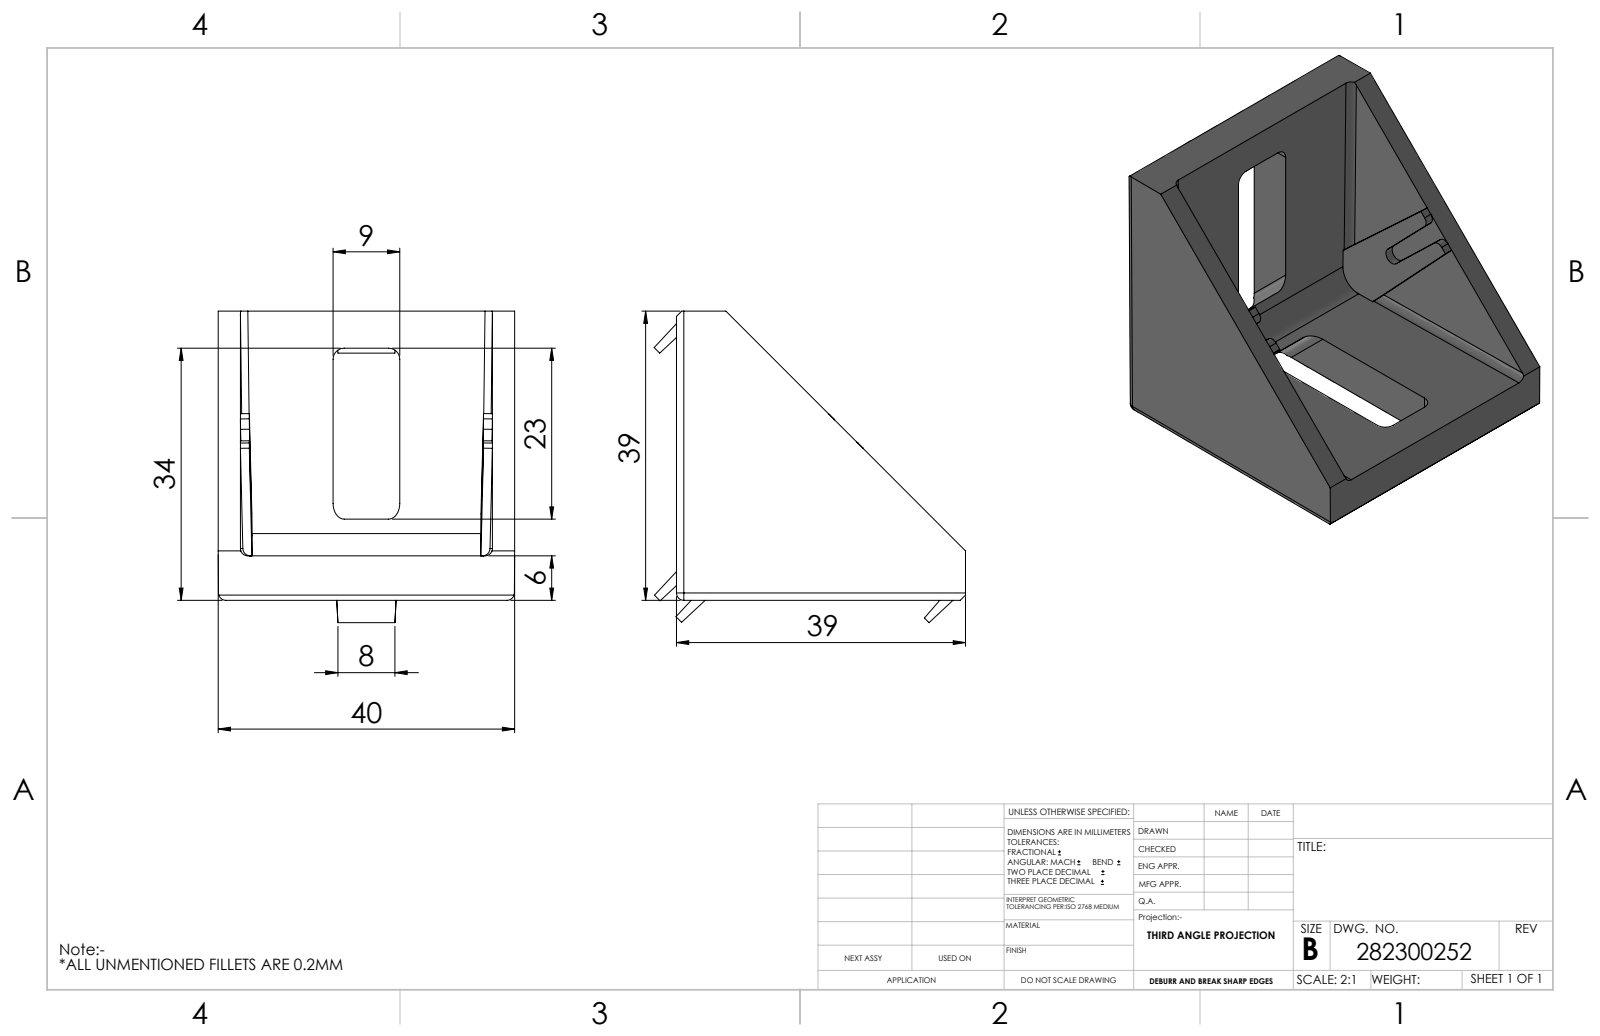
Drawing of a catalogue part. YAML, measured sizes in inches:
part_name: "282300252"
step_written_by: "SolidWorks 2014 (AUTOMOTIVE_DESIGN)"
units: inches
bodies: {solids: 1, faces: 189, planar: 103, cylindrical: 68, other: 18}
overall_size: [2.132, 1.575, 1.335]
volume: 0.914
surface_area: 15.96
round_bosses_or_shafts:
  - {diameter: 0.157, count: 4}
partial_cylinders:
  - {radius: 0.039, count: 33}
  - {radius: 0.02, count: 12}
  - {radius: 0.059, count: 8}
  - {radius: 0.044, count: 2}
  - {radius: 0.118, count: 1}
face_to_face_distances: [0.118, 0.236, 1.299, 1.417, 1.535, 1.023, 0.354, 0.047, 0.213, 0.079]
